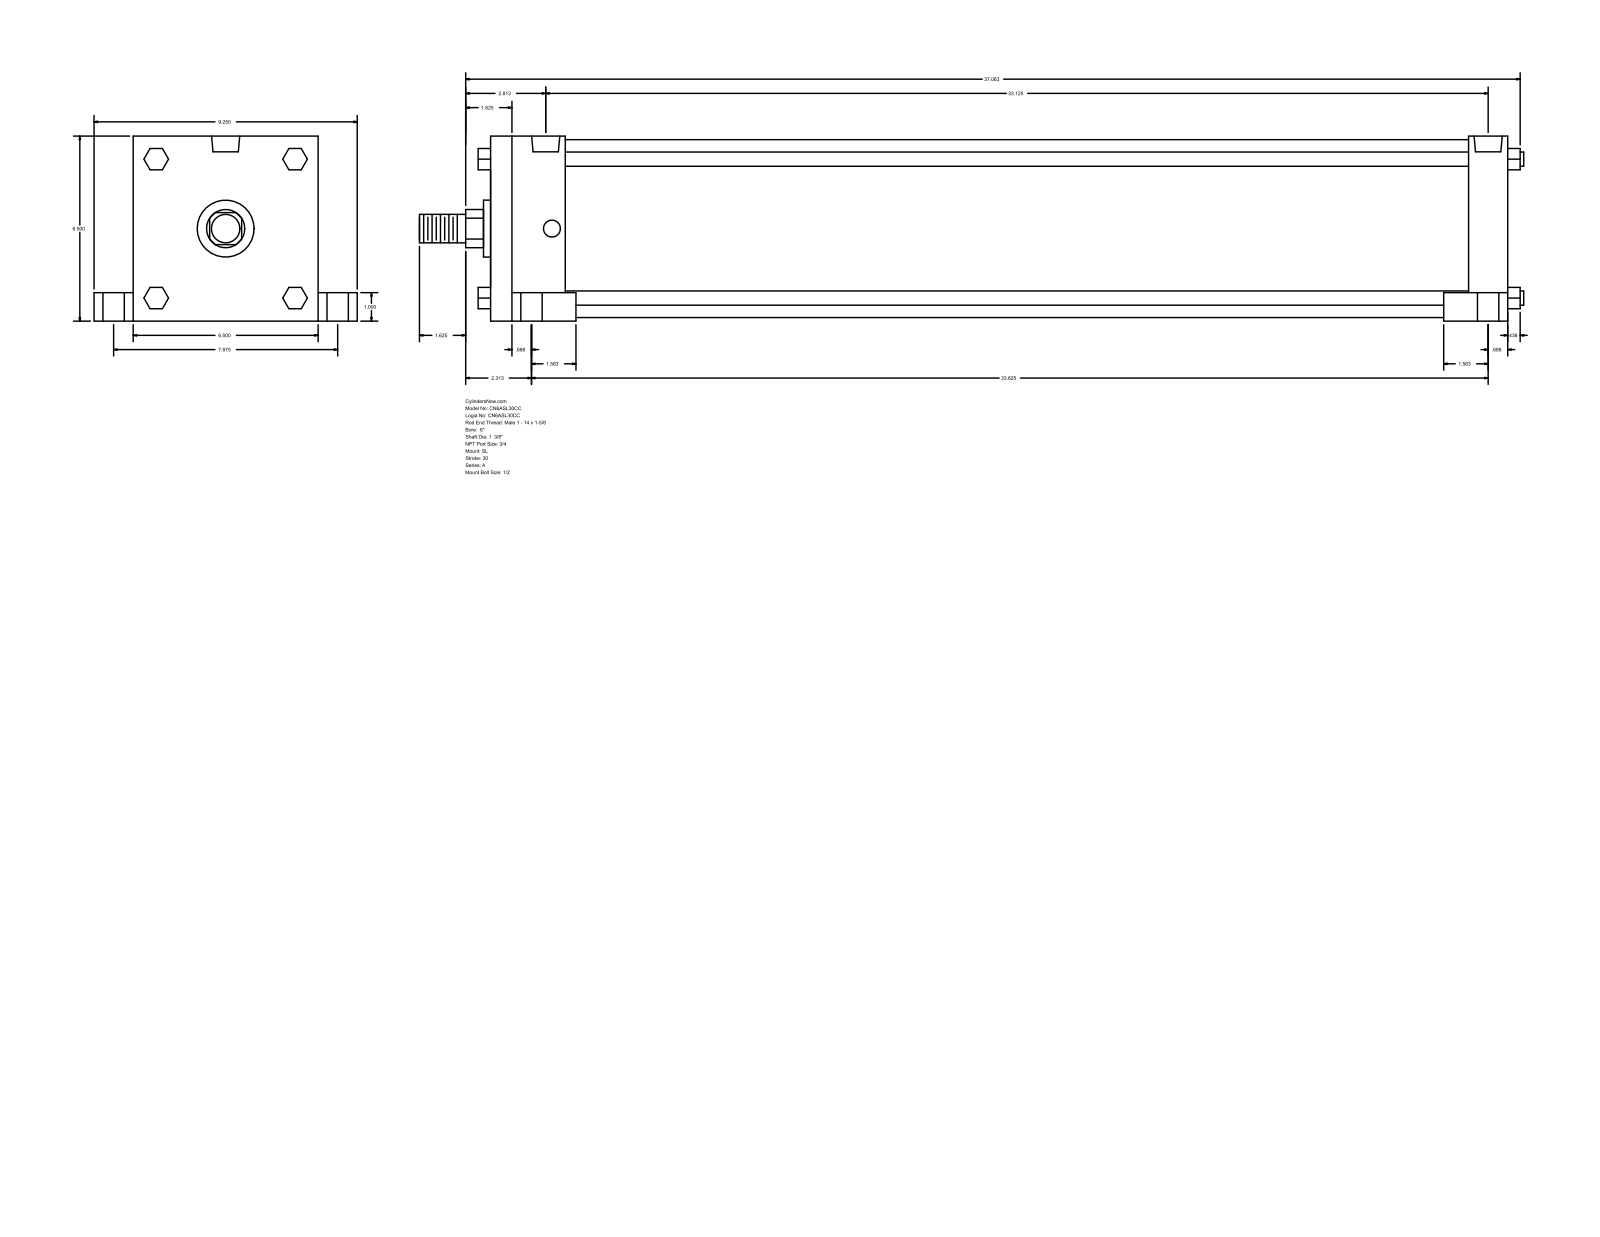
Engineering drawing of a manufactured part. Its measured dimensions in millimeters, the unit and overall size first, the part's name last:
Units: millimetres
Overall size (bounding box): 985.84 × 234.95 × 165.1
Round holes (diameter × count): ⌀15.08 ×4, ⌀19.05 ×4, ⌀25.4 ×4, ⌀25.12 ×2
Round bosses / shafts (diameter × count): ⌀12.7 ×4, ⌀158.75 ×1, ⌀50.8 ×1, ⌀34.92 ×1, ⌀25.4 ×1
Partial cylindrical surfaces — rounded edges, fillets, slot ends (radius × count): R17.06 ×1
Main face-to-face distances: 165.1, 908.04, 34.92, 873.12, 66.67, 841.37, 806.45, 25.4, 139.7, 200.02
Hole centre spacings: 5.56, 100.01, 100.16, 100.81, 101.66, 200.02, 830.25, 835.81
Bodies: 0 solids, 150 faces (114 planar, 36 cylindrical, 0 other)
Part name (STEP PRODUCT): A_SL__0600_1.375
STEP written by: GSSL Pune (CONFIG_CONTROL_DESIGN)
